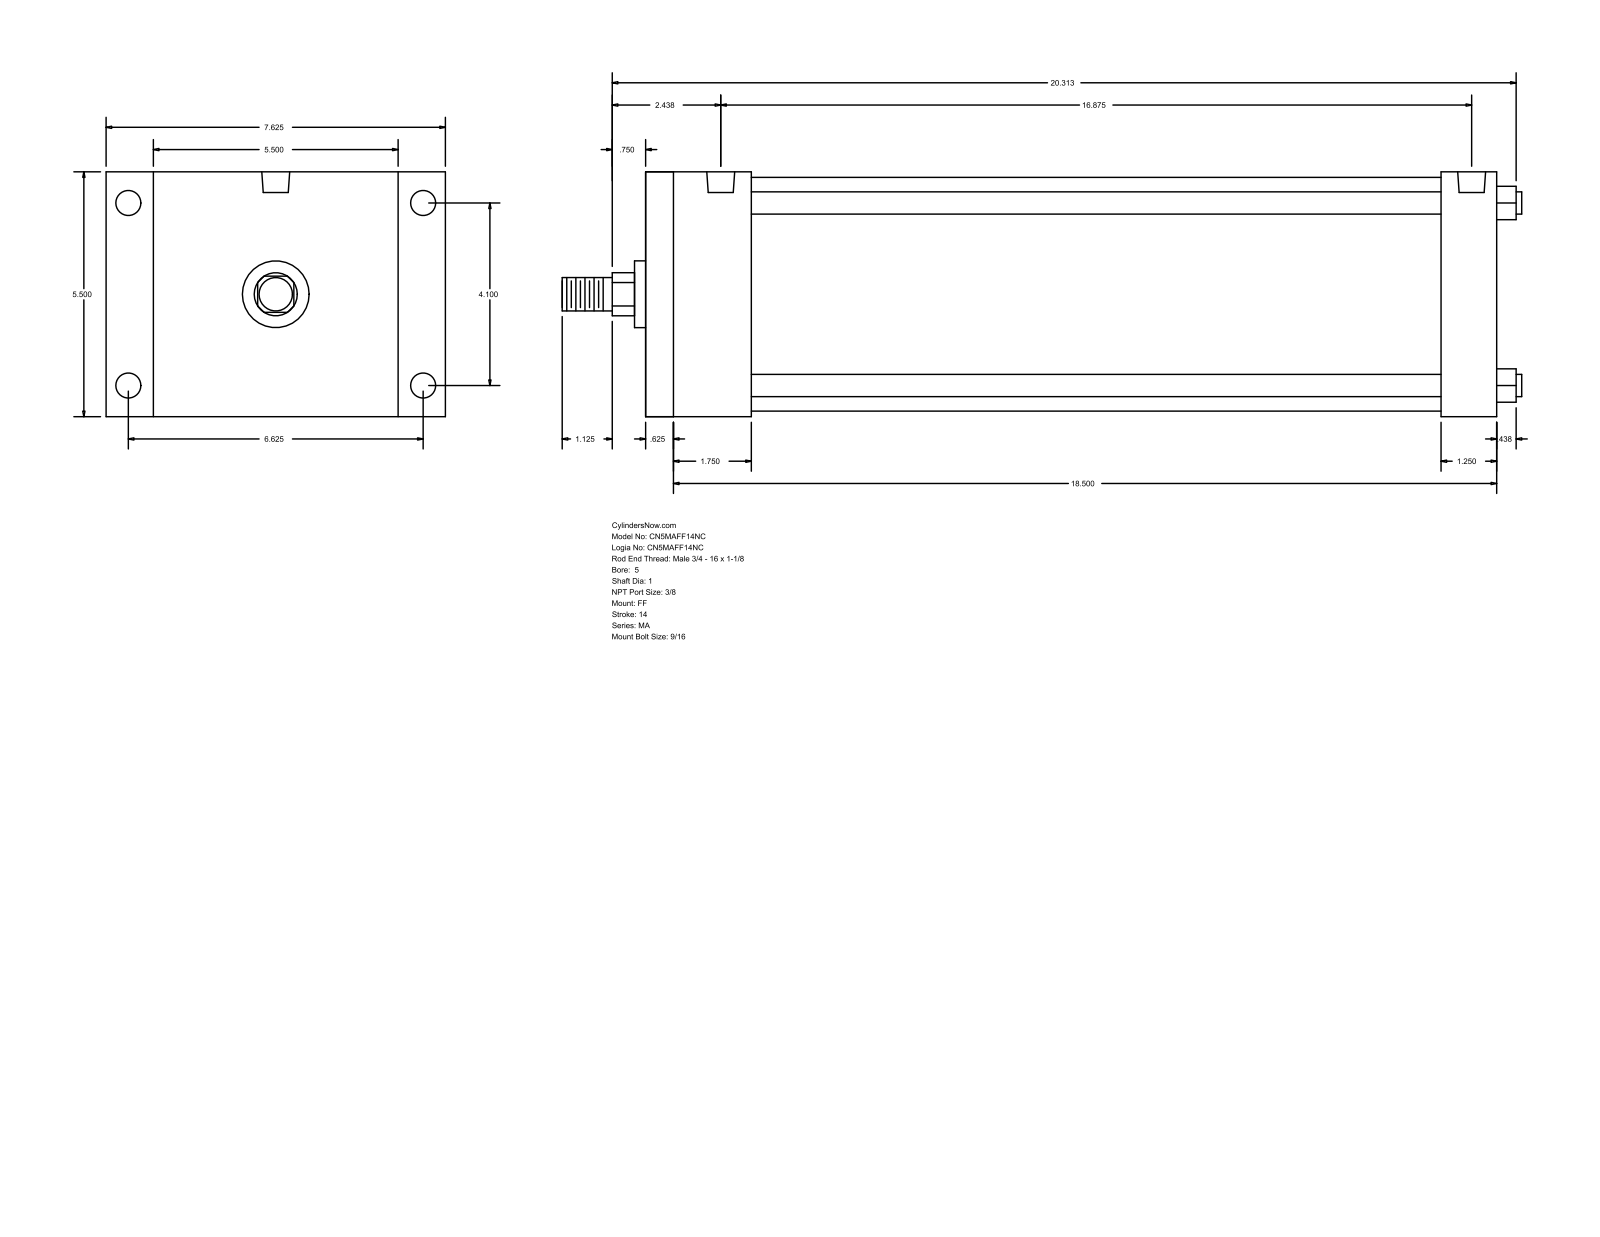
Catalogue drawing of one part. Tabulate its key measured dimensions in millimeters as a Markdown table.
| quantity | value |
| --- | --- |
| part name | MA_FF__0500_1 |
| STEP written by | GSSL Pune (CONFIG_CONTROL_DESIGN) |
| units | millimeters |
| bodies | 0 solids, 92 faces (64 planar, 28 cylindrical, 0 other) |
| overall size | 547.69 × 193.68 × 139.7 |
| round holes (diameter × count) | 11.11 × 4, 14.29 × 4, 15.93 × 2 |
| round bosses / shafts (diameter × count) | 12.7 × 4, 133.35 × 1, 38.1 × 1, 25.4 × 1, 19.05 × 1 |
| partial cylindrical surfaces (radius × count) | 12.29 × 1 |
| main face-to-face distances | 139.7, 485.77, 15.87, 469.9, 454.02, 438.15, 31.75, 60.33, 44.46, 393.69 |
| hole center spacings | 104.14, 168.28, 197.9, 419.1, 4.76, 4.77, 423.86, 423.87 |
